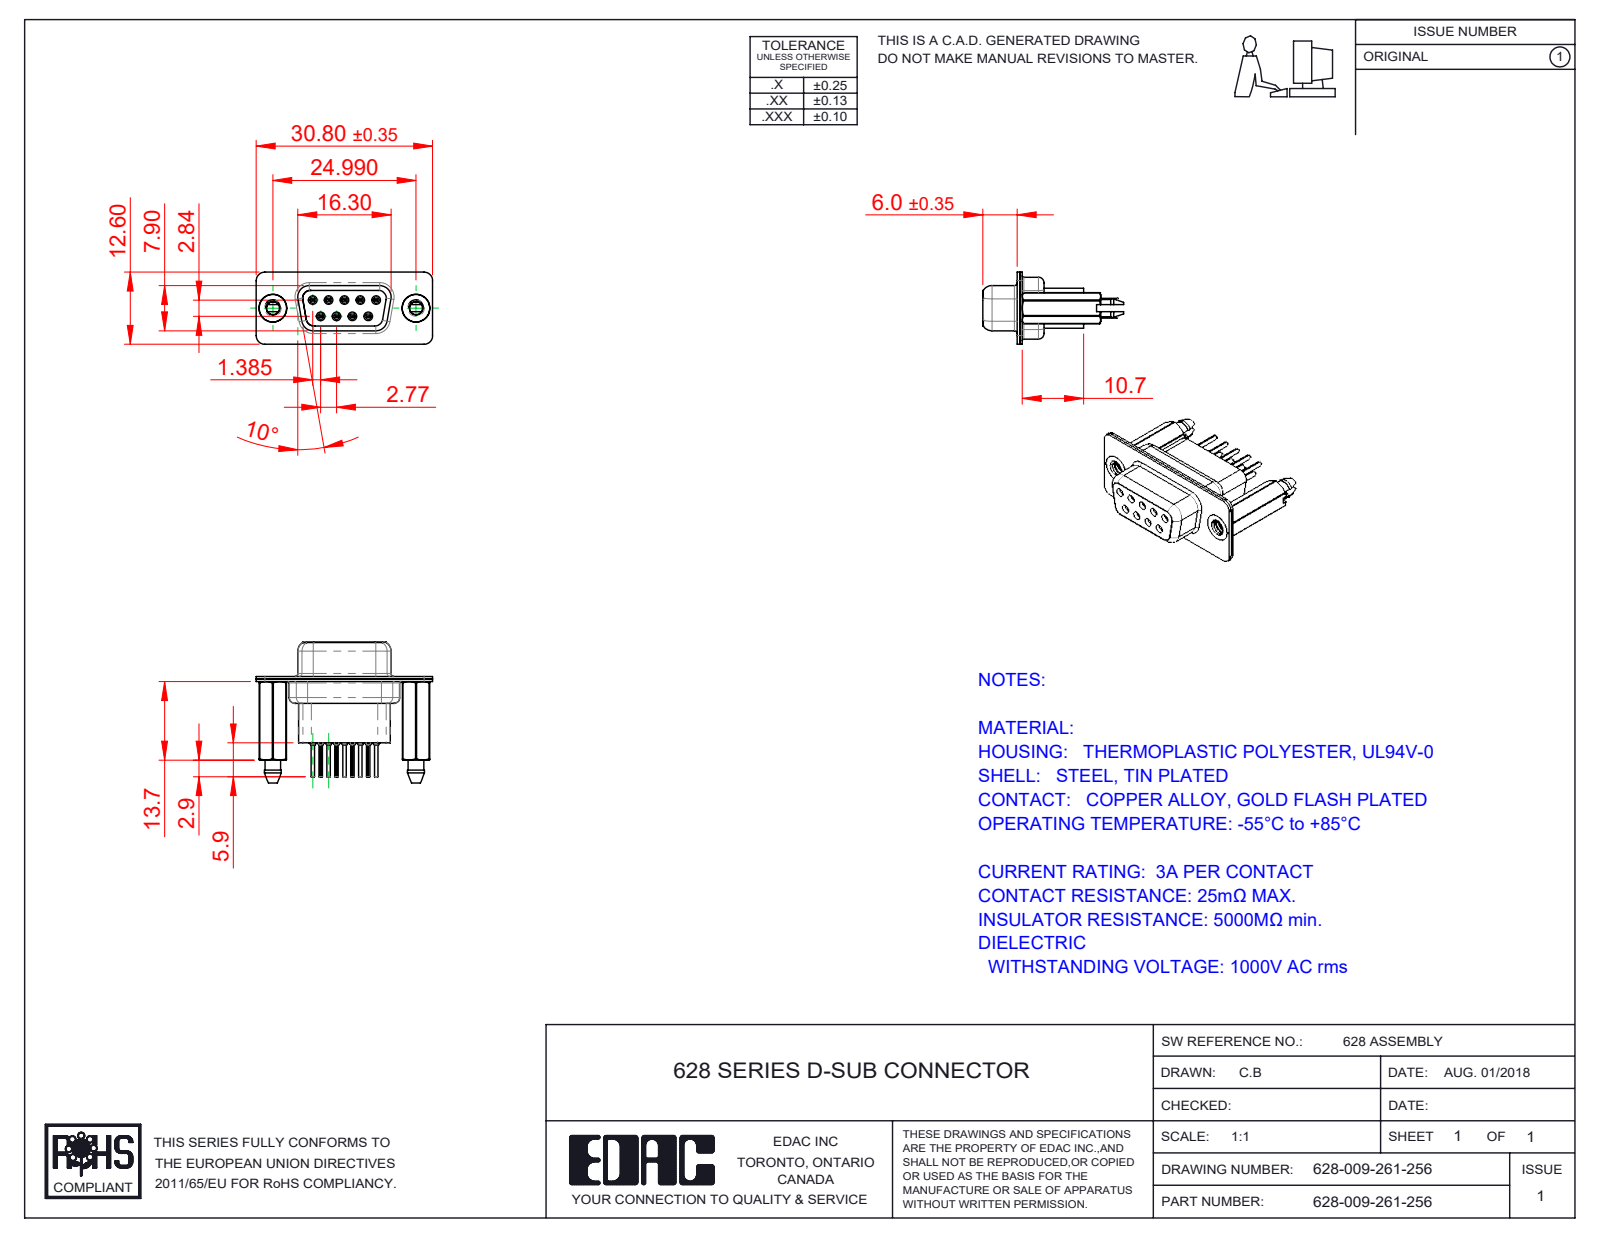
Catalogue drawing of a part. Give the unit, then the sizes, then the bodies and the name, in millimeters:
Units: millimetres
Overall size (bounding box): 30.8 × 24.6 × 12.6
Round holes (diameter × count): ⌀0.2 ×9, ⌀0.8 ×9, ⌀0.9 ×9, ⌀1.1 ×9, ⌀1.6 ×9, ⌀1.7 ×5, ⌀2.26 ×2, ⌀4 ×2, ⌀4.05 ×2, ⌀4.85 ×2
Round bosses / shafts (diameter × count): ⌀2 ×9, ⌀1.5 ×9, ⌀1.2 ×9, ⌀0.6 ×9, ⌀4.95 ×2, ⌀4.8 ×2
Partial cylindrical surfaces — rounded edges, fillets, slot ends (radius × count): R1.5 ×19, R0.1 ×18, R2 ×12, R0.28 ×9, R1.35 ×6, R1.6 ×6, R0.25 ×4, R0.5 ×4
Main face-to-face distances: 0.45, 0.4, 0.9, 8.5, 6.6, 1.9, 1.4, 4.76, 7, 10.7
Hole centre spacings: 3.16, 2.77, 5.54, 5.03, 5.04, 8.31, 7.48, 7.49
Volume: 2 591 mm³ · Surface area: 6 029 mm²
Bodies: 14 solids, 1460 faces (378 planar, 466 cylindrical, 616 other)
Part name (STEP PRODUCT): 628 Shell Front_09 Contacts; 628 Shell Rear_09 Contacts; 628 Contact Row 1_61; 628-009-261-256 (+3 more)
STEP written by: SolidWorks 2020 (CONFIG_CONTROL_DESIGN)
